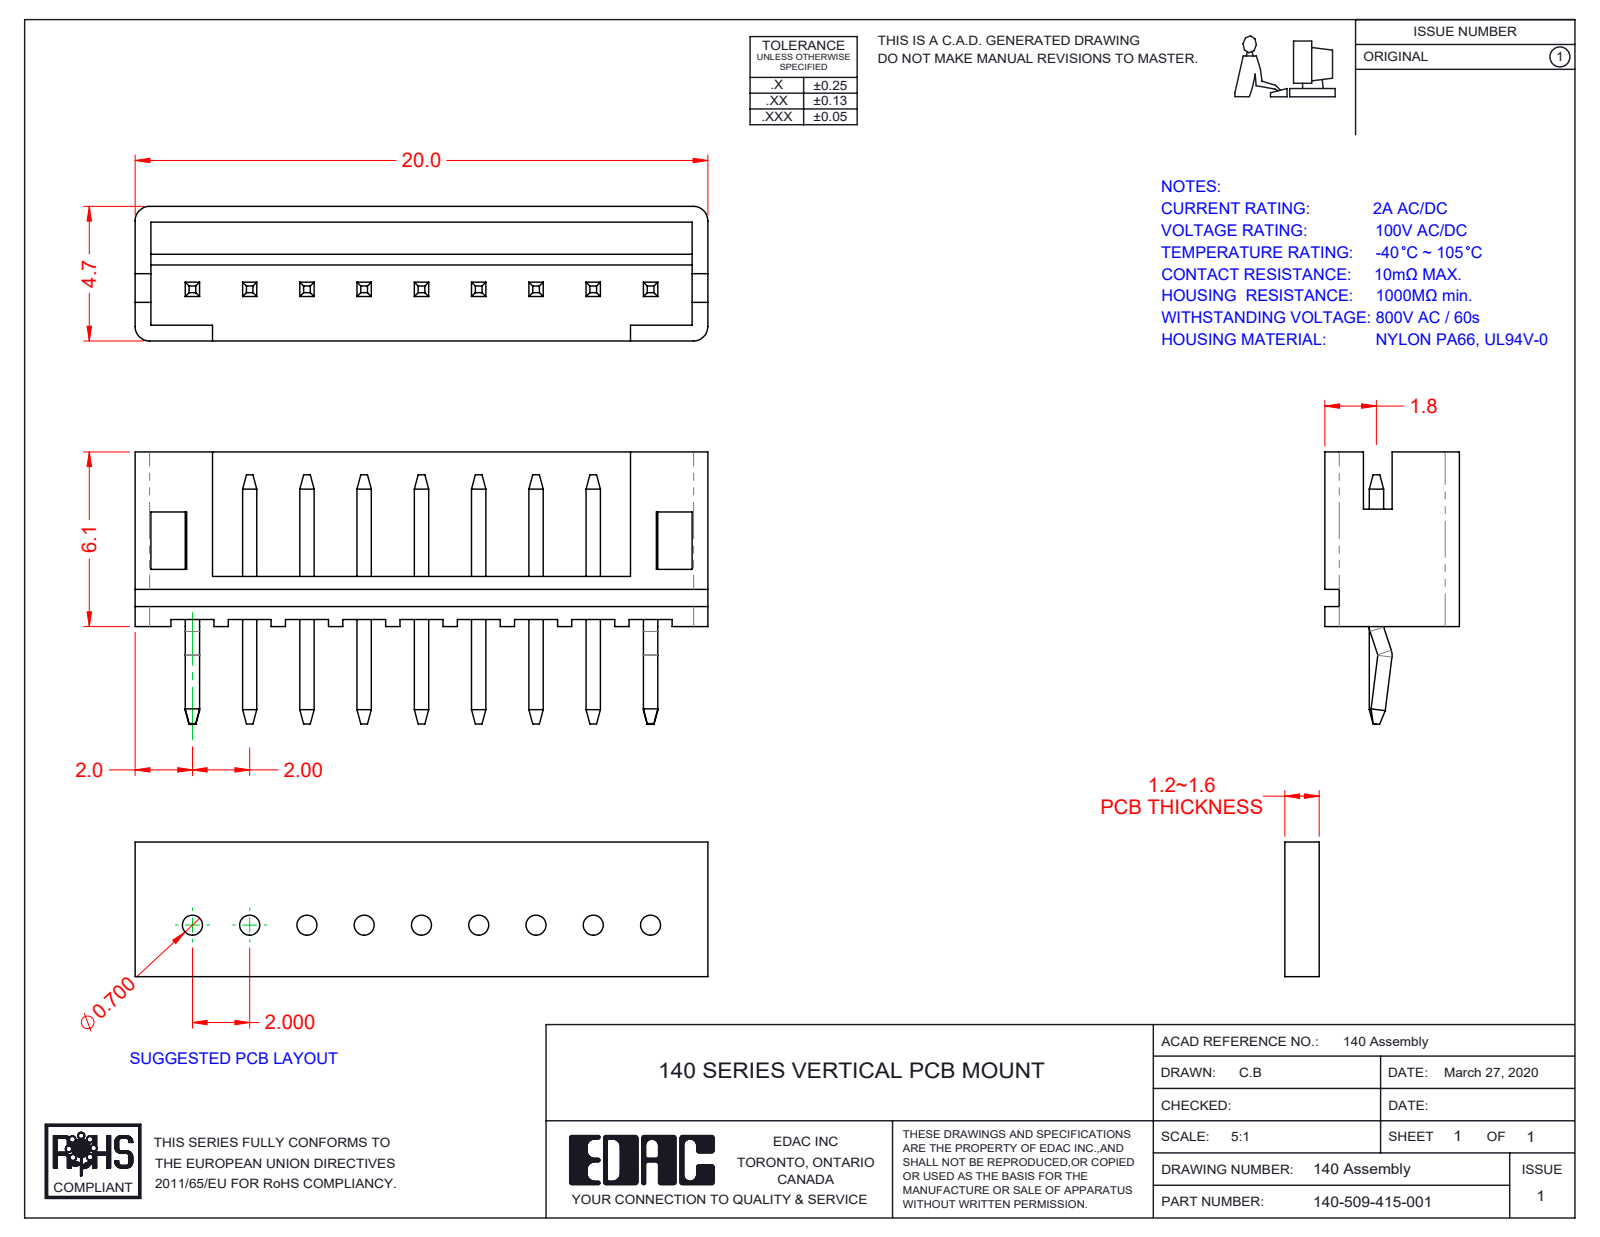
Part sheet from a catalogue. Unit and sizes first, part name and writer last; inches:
Units: inches
Overall size (bounding box): 0.787 × 0.375 × 0.185
Partial cylindrical surfaces — rounded edges, fillets, slot ends (radius × count): R0.02 ×4, R0.022 ×1
Main face-to-face distances: 0.022, 0.059, 0.02, 0.079, 0.157, 0.163, 0.236, 0.061, 0.069, 0.083
Volume: 0.013 in³ · Surface area: 1.21 in²
Bodies: 10 solids, 268 faces (250 planar, 16 cylindrical, 2 other)
Part name (STEP PRODUCT): V Housing_509; V Contact_Kink; 140-509-415-001; V Contact_Str
STEP written by: SolidWorks 2016 (CONFIG_CONTROL_DESIGN)
